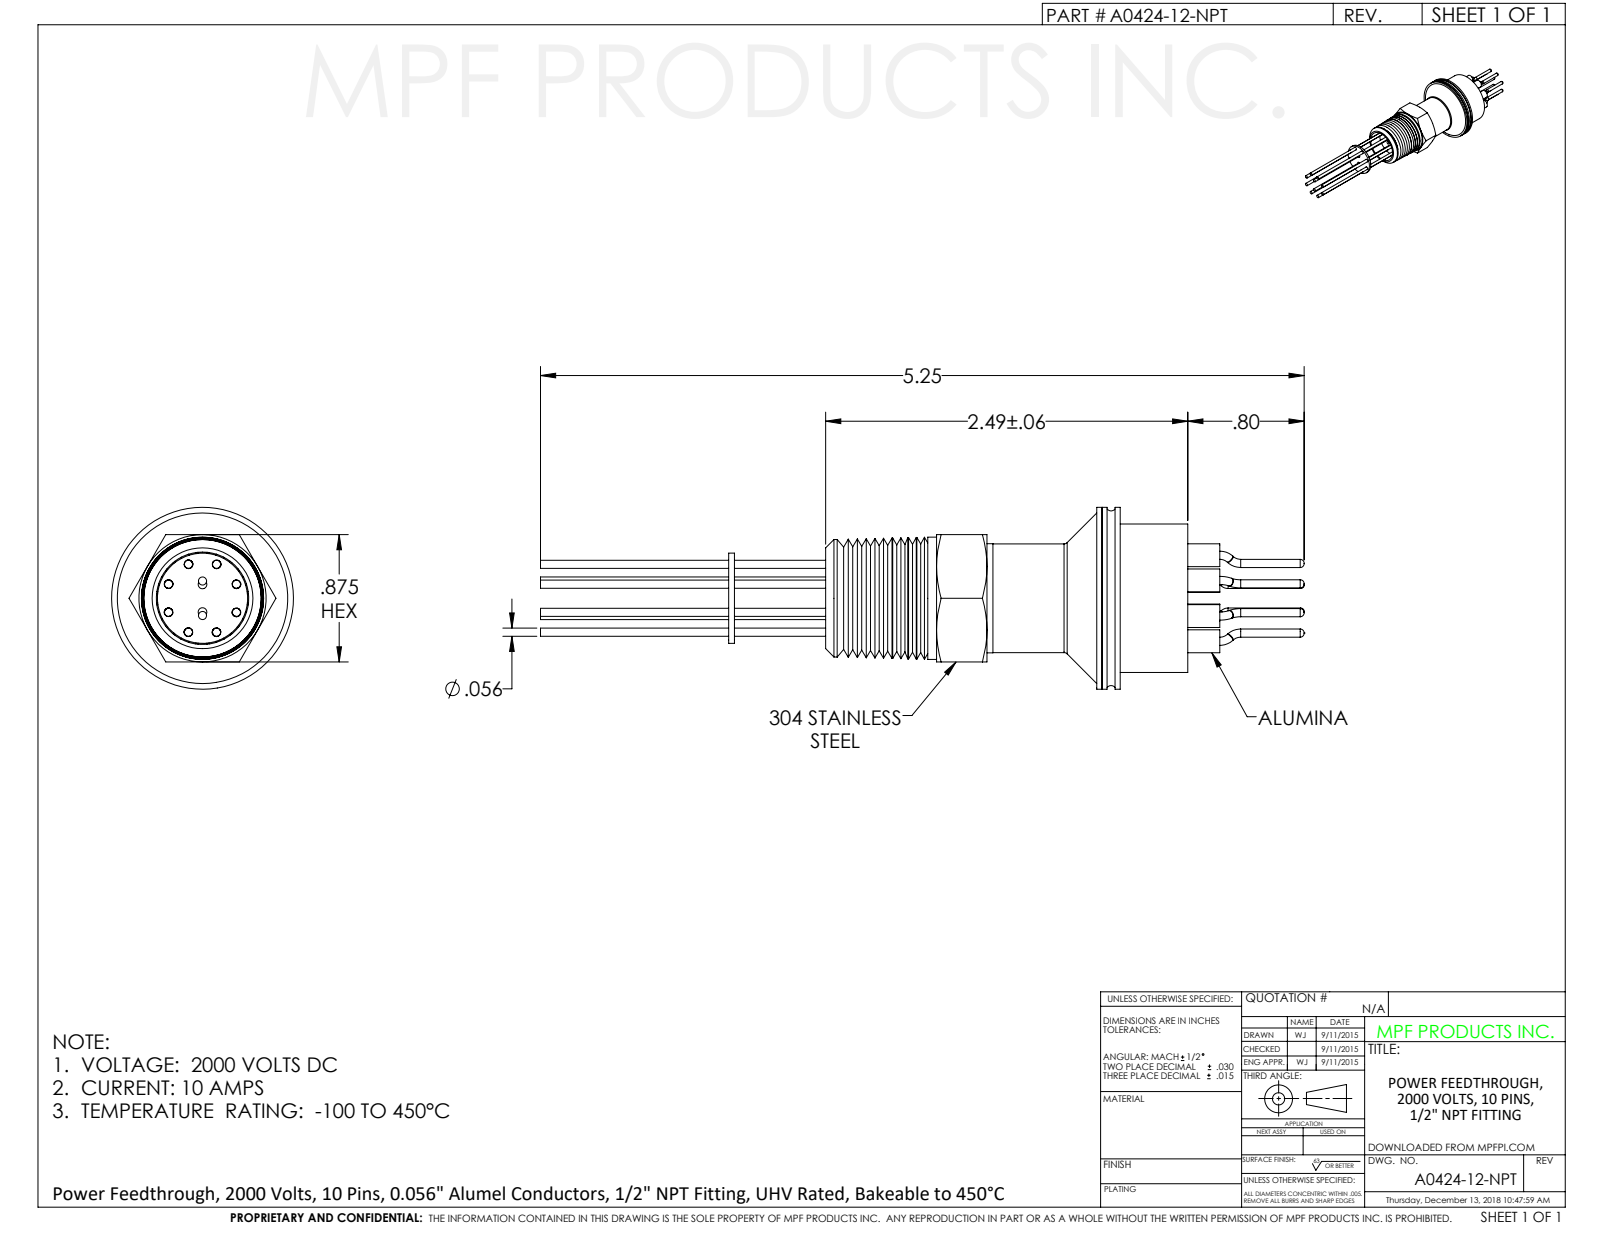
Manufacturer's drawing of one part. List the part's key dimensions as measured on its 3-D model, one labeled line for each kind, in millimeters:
Part name (STEP PRODUCT): A0424-12-NPT
STEP written by: SolidWorks 2012 (CONFIG_CONTROL_DESIGN)
Units: millimetres
Bodies: 1 solid, 518 faces (71 planar, 230 cylindrical, 217 other)
Overall size (bounding box): 133.4 × 31.8 × 31.8
Volume: 12 400 mm³ · Surface area: 19 860 mm²
Round holes (diameter × count): ⌀4 ×10, ⌀15.9 ×1, ⌀17.1 ×1, ⌀23.9 ×1, ⌀24.4 ×1, ⌀24.6 ×1
Round bosses / shafts (diameter × count): ⌀1.4 ×30, ⌀4.7 ×10, ⌀4.3 ×10, ⌀31.8 ×1, ⌀25.9 ×1, ⌀24.3 ×1, ⌀21.3 ×1, ⌀19.1 ×1
Main face-to-face distances: 1, 16.3, 1.3, 10.9, 9.7, 22.2, 3.2, 14.1, 83.2, 92.8
Hole centre spacings: 3.3, 6.2, 6.8, 9.7, 11.5, 12, 12, 13
